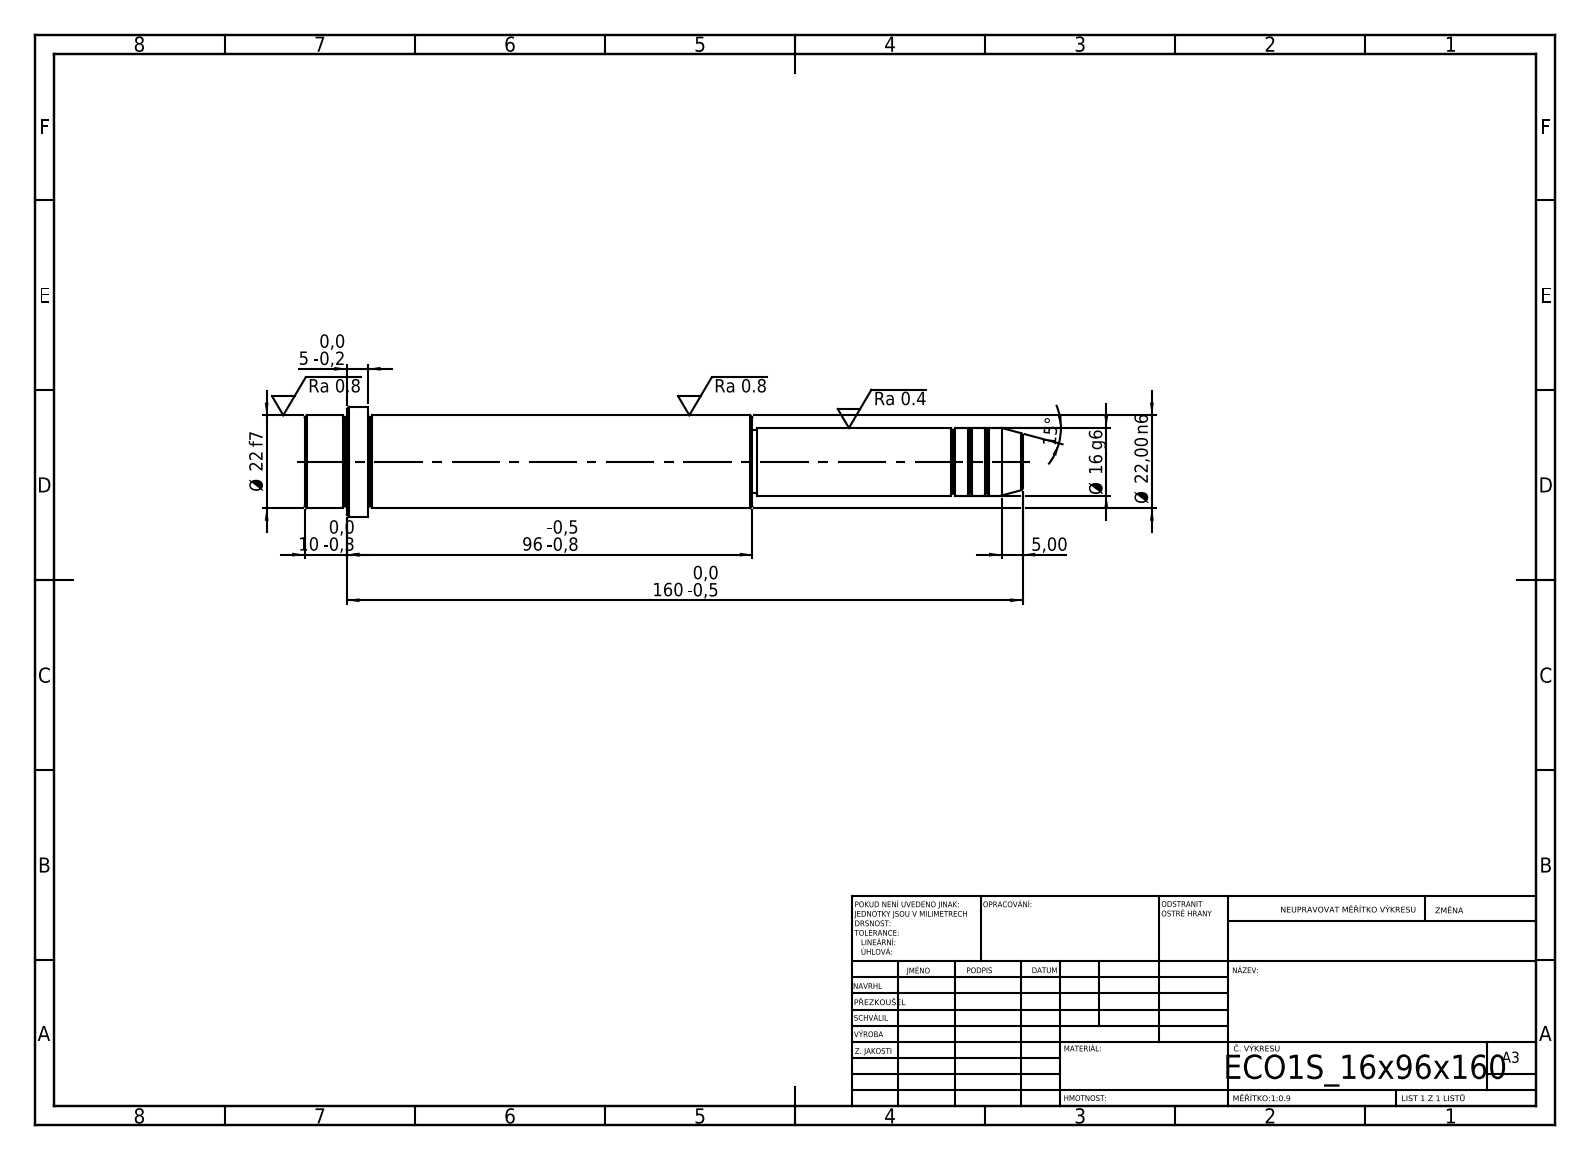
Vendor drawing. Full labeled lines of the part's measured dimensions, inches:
STEP written by: SolidWorks 2019 (CONFIG_CONTROL_DESIGN)
Units: inches
Bodies: 1 solid, 52 faces (6 planar, 16 cylindrical, 30 other)
Overall size (bounding box): 6.693 × 1.024 × 1.024
Volume: 3.271 in³ · Surface area: 18.16 in²
Round bosses / shafts (diameter × count): ⌀1.024 ×1, ⌀0.866 ×1, ⌀0.63 ×1, ⌀0.591 ×1
Main face-to-face distances: 4.173, 3.583, 0.591, 2.52, 6.102, 6.693, 6.299, 3.78, 0.197, 0.394
